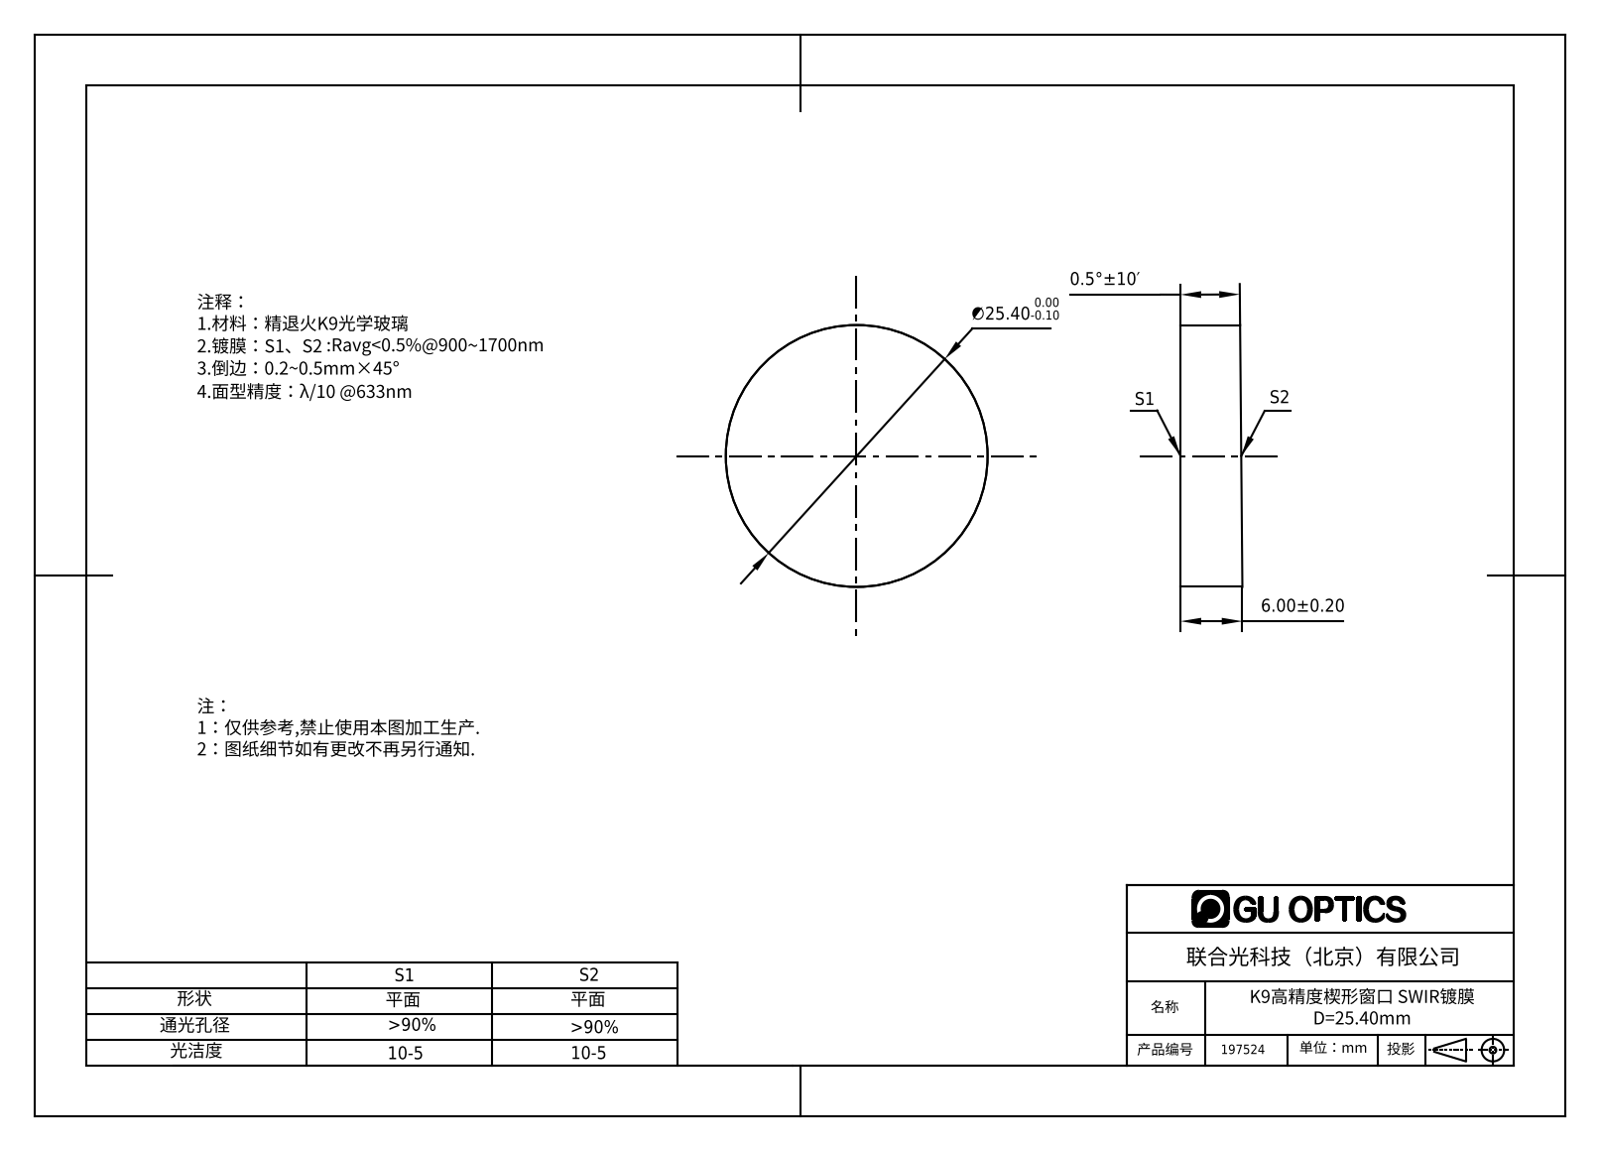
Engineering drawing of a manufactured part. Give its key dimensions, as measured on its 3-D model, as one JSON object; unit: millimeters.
{"part_name": "197503", "step_written_by": "SolidWorks 2016 (AUTOMOTIVE_DESIGN)", "units": "millimeters", "bodies": {"solids": 1, "faces": 4, "planar": 2, "cylindrical": 2, "other": 0}, "overall_size": [25.4, 25.4, 6], "volume_mm3": 2984, "surface_area_mm2": 1483, "round_bosses_or_shafts": [[25.4, 1]]}
